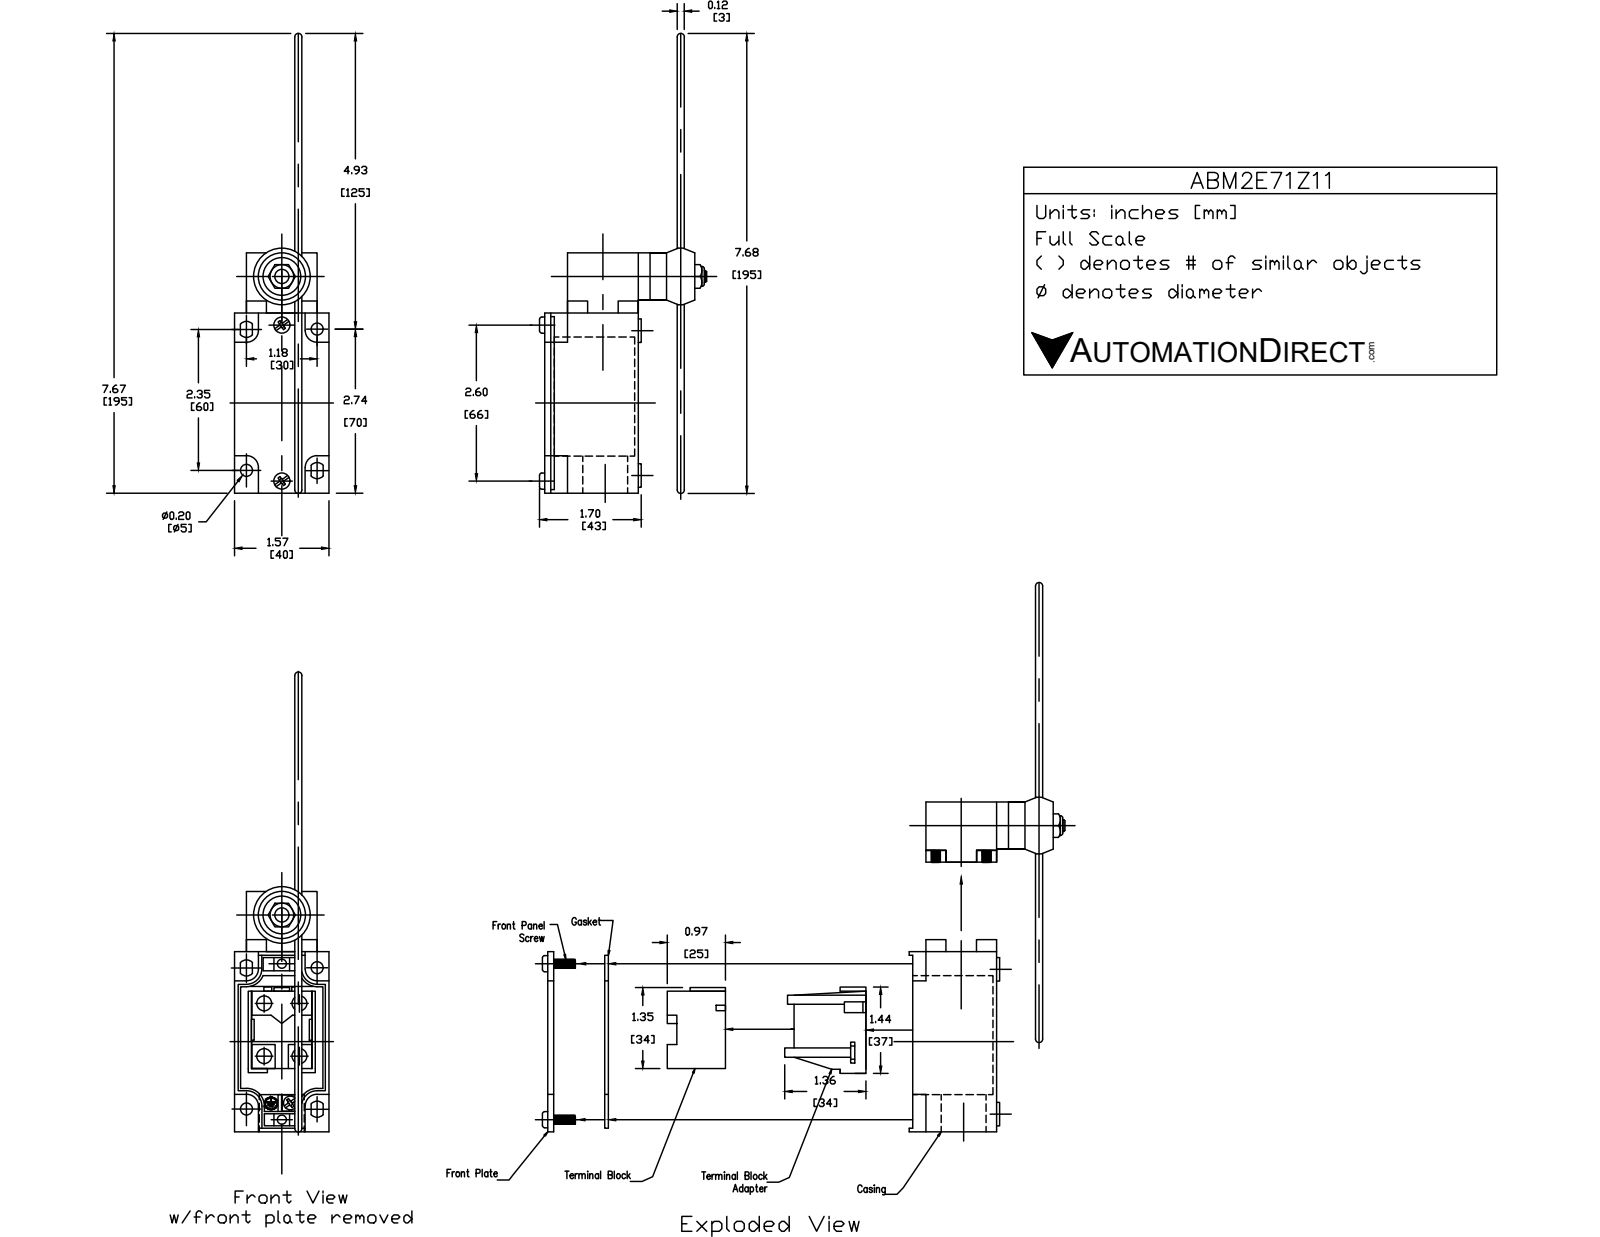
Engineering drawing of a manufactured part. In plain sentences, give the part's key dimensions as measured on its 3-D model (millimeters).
The part is named "ABM2E71Z11". Its 3-D file was written by "SolidWorks 2017 (AUTOMOTIVE_DESIGN)". It is 5 solids with 238 faces: 116 planar, 89 cylindrical and 33 other. Overall it measures 194.9 by 59.3 by 40 millimeters. Its volume is 141 600 cubic millimeters and its surface area 29 600 square millimeters. Round holes: 2 of diameter 5.2, 1 of diameter 3, 1 of diameter 6, 1 of diameter 14, 1 of diameter 17, 1 of diameter 19. Round bosses or shafts: 5 of diameter 10, 2 of diameter 7, 1 of diameter 24, 1 of diameter 20, 1 of diameter 6. Partial cylindrical surfaces (rounded edges, fillets, slot ends): 16 of radius 1.5, 4 of radius 1, 4 of radius 5, 2 of radius 3.3, 1 of radius 11.5, 1 of radius 12. The main face-to-face distances are 40, 39.5, 5, 30, 35, 76.5, 25, 9.5, 4.5, 102. The hole center spacings are 35.4, 14, 26.6, 67.1, 83.4.
